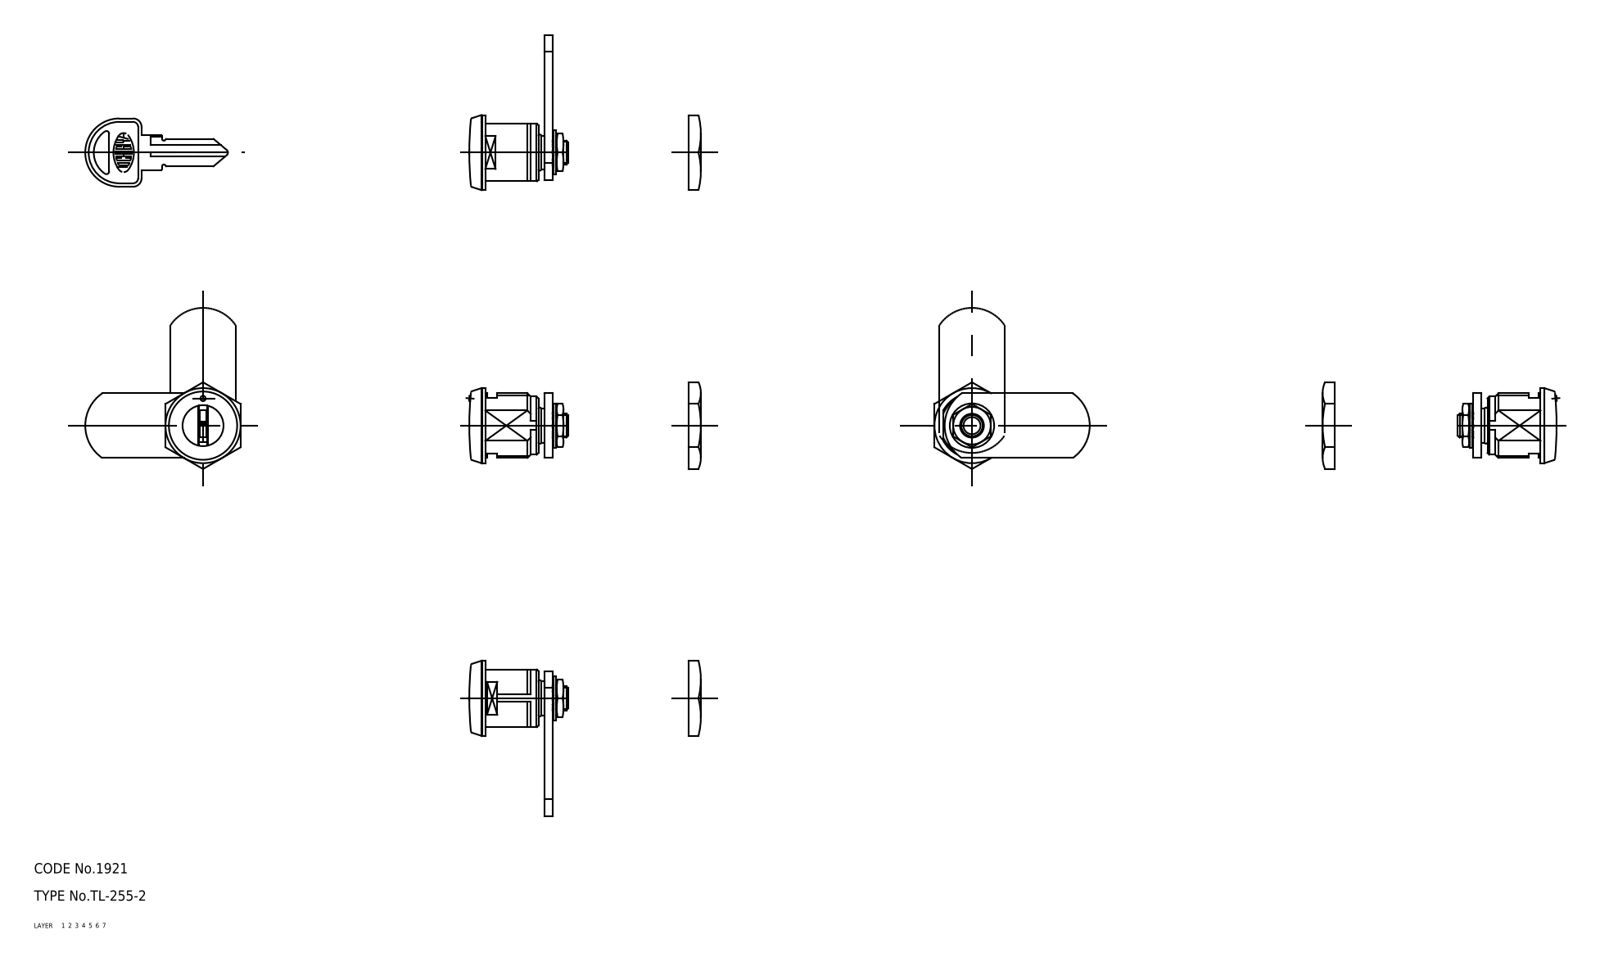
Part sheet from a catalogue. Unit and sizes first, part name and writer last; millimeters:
Units: millimetres
Overall size (bounding box): 110.4 × 45.5 × 25.4
Volume: 8 811 mm³ · Surface area: 7 235 mm²
Bodies: 7 solids, 160 faces (0 planar, 0 cylindrical, 160 other)
Part name (STEP PRODUCT): washer; nut_B; nut_A; lock (+4 more)
STEP written by: CADfix (AUTOMOTIVE_DESIGN)
